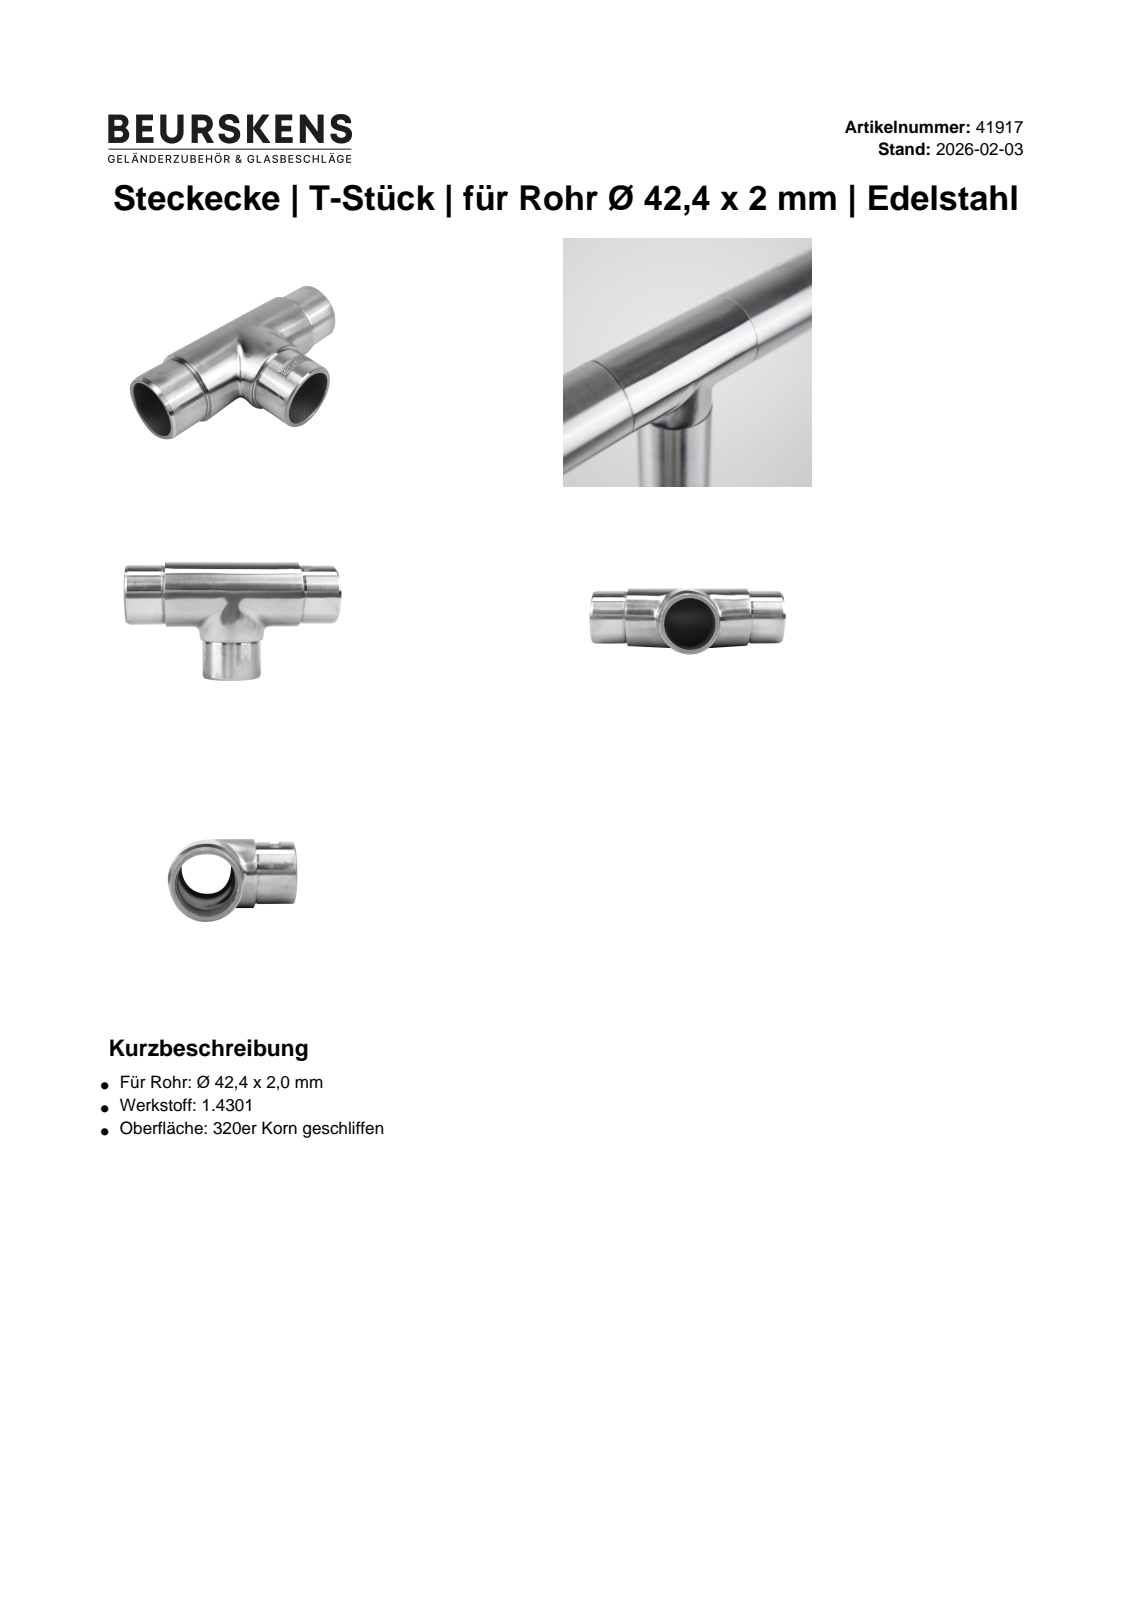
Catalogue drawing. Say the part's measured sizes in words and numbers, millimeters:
The part is named "41917". Its 3-D file was written by "Autodesk Inventor 2022 (AUTOMOTIVE_DESIGN)". It is 1 solid with 19 faces: 9 planar, 10 cylindrical and 0 other. Overall it measures 135 by 75 by 42.4 millimeters. Its volume is 40 849 cubic millimeters and its surface area 41 521 square millimeters. Round holes: 2 of diameter 34.2, 2 of diameter 38.4. Round bosses or shafts: 2 of diameter 42.4, 2 of diameter 38.2. The main face-to-face distances are 2, 27, 25, 83, 108, 110, 85, 81, 135.
